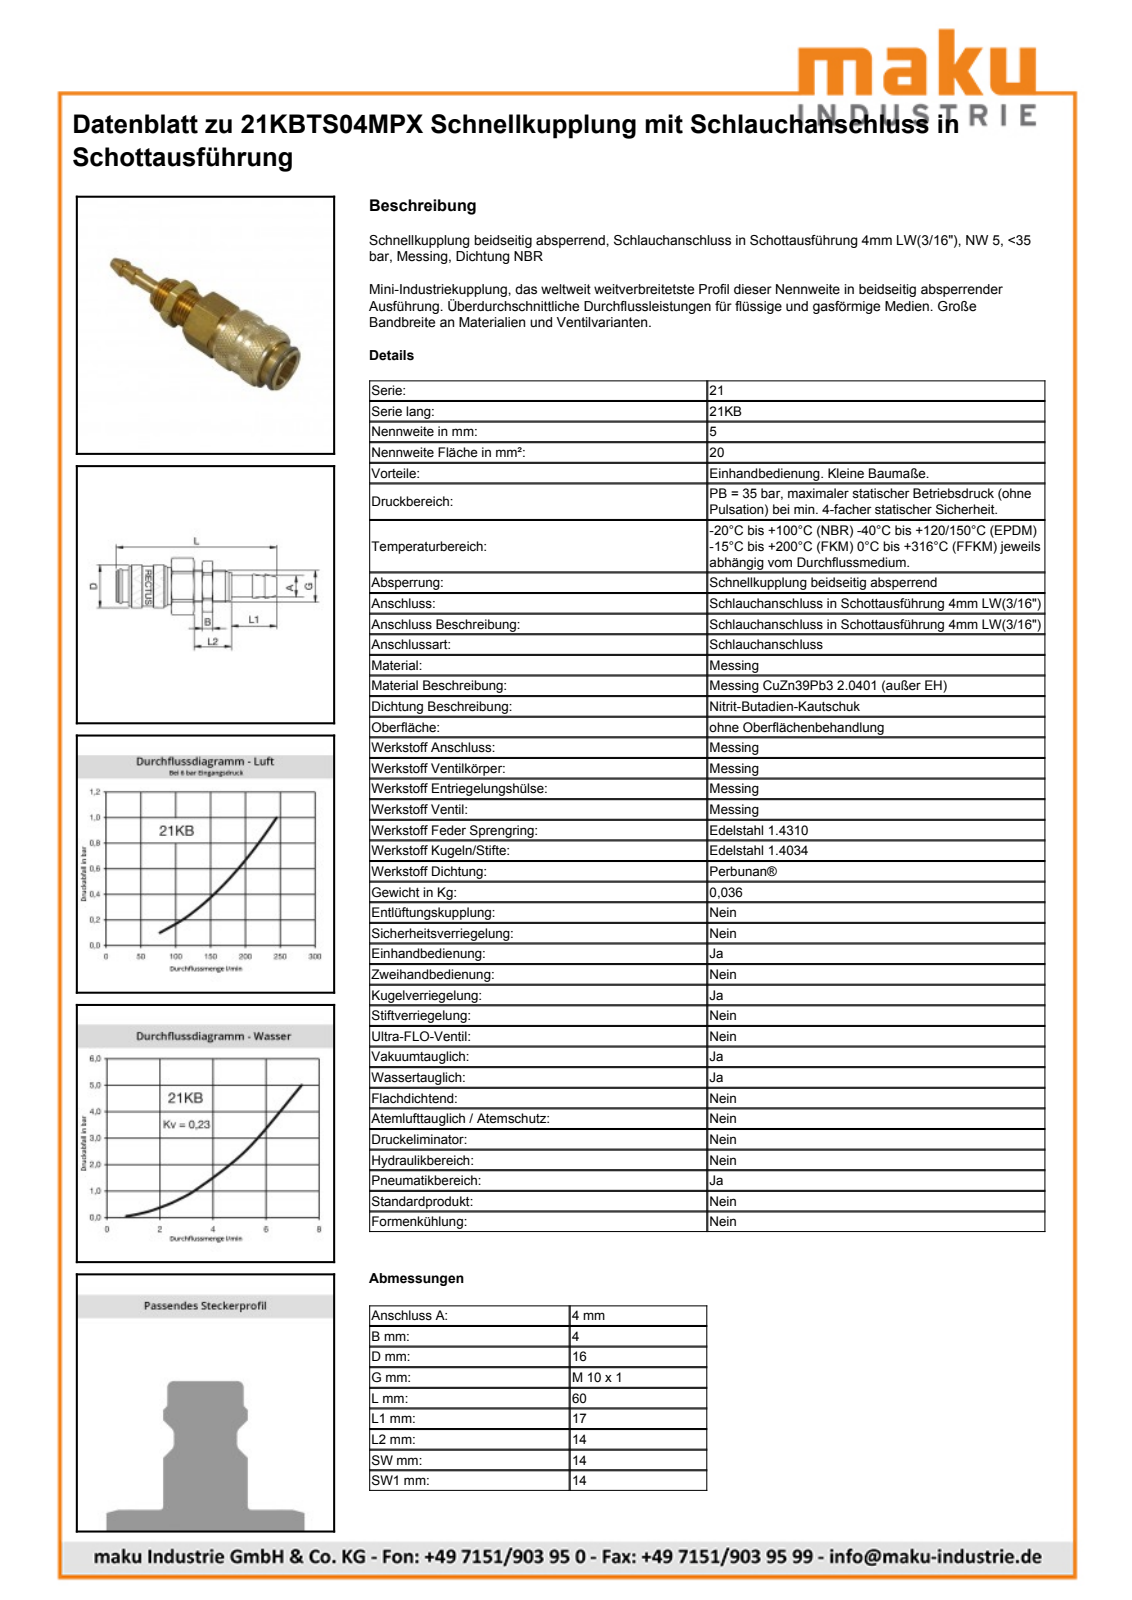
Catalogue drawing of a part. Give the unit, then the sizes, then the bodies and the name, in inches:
Units: inches
Overall size (bounding box): 2.348 × 0.636 × 0.636
Round holes (diameter × count): ⌀0.079 ×1, ⌀0.177 ×1, ⌀0.323 ×1, ⌀0.354 ×1, ⌀0.394 ×1, ⌀0.409 ×1, ⌀0.411 ×1, ⌀0.421 ×1, ⌀0.453 ×1, ⌀0.478 ×1, ⌀0.551 ×1
Round bosses / shafts (diameter × count): ⌀0.636 ×1, ⌀0.594 ×1, ⌀0.472 ×1, ⌀0.449 ×1, ⌀0.439 ×1, ⌀0.339 ×1, ⌀0.159 ×1
Partial cylindrical surfaces — rounded edges, fillets, slot ends (radius × count): R0.266 ×1, R0.293 ×1, R0.311 ×1
Main face-to-face distances: 0.551, 0.512, 0.039, 0.079, 0.907, 0.472, 0.829, 0.396, 0.433, 0.287
Volume: 0.234 in³ · Surface area: 9.013 in²
Bodies: 5 solids, 507 faces (162 planar, 72 cylindrical, 273 other)
Part name (STEP PRODUCT): VOX21XXXMXX; GST21S04MXX; D108978; D103523 (+2 more)
STEP written by: Autodesk Inventor 2016 (AUTOMOTIVE_DESIGN)
